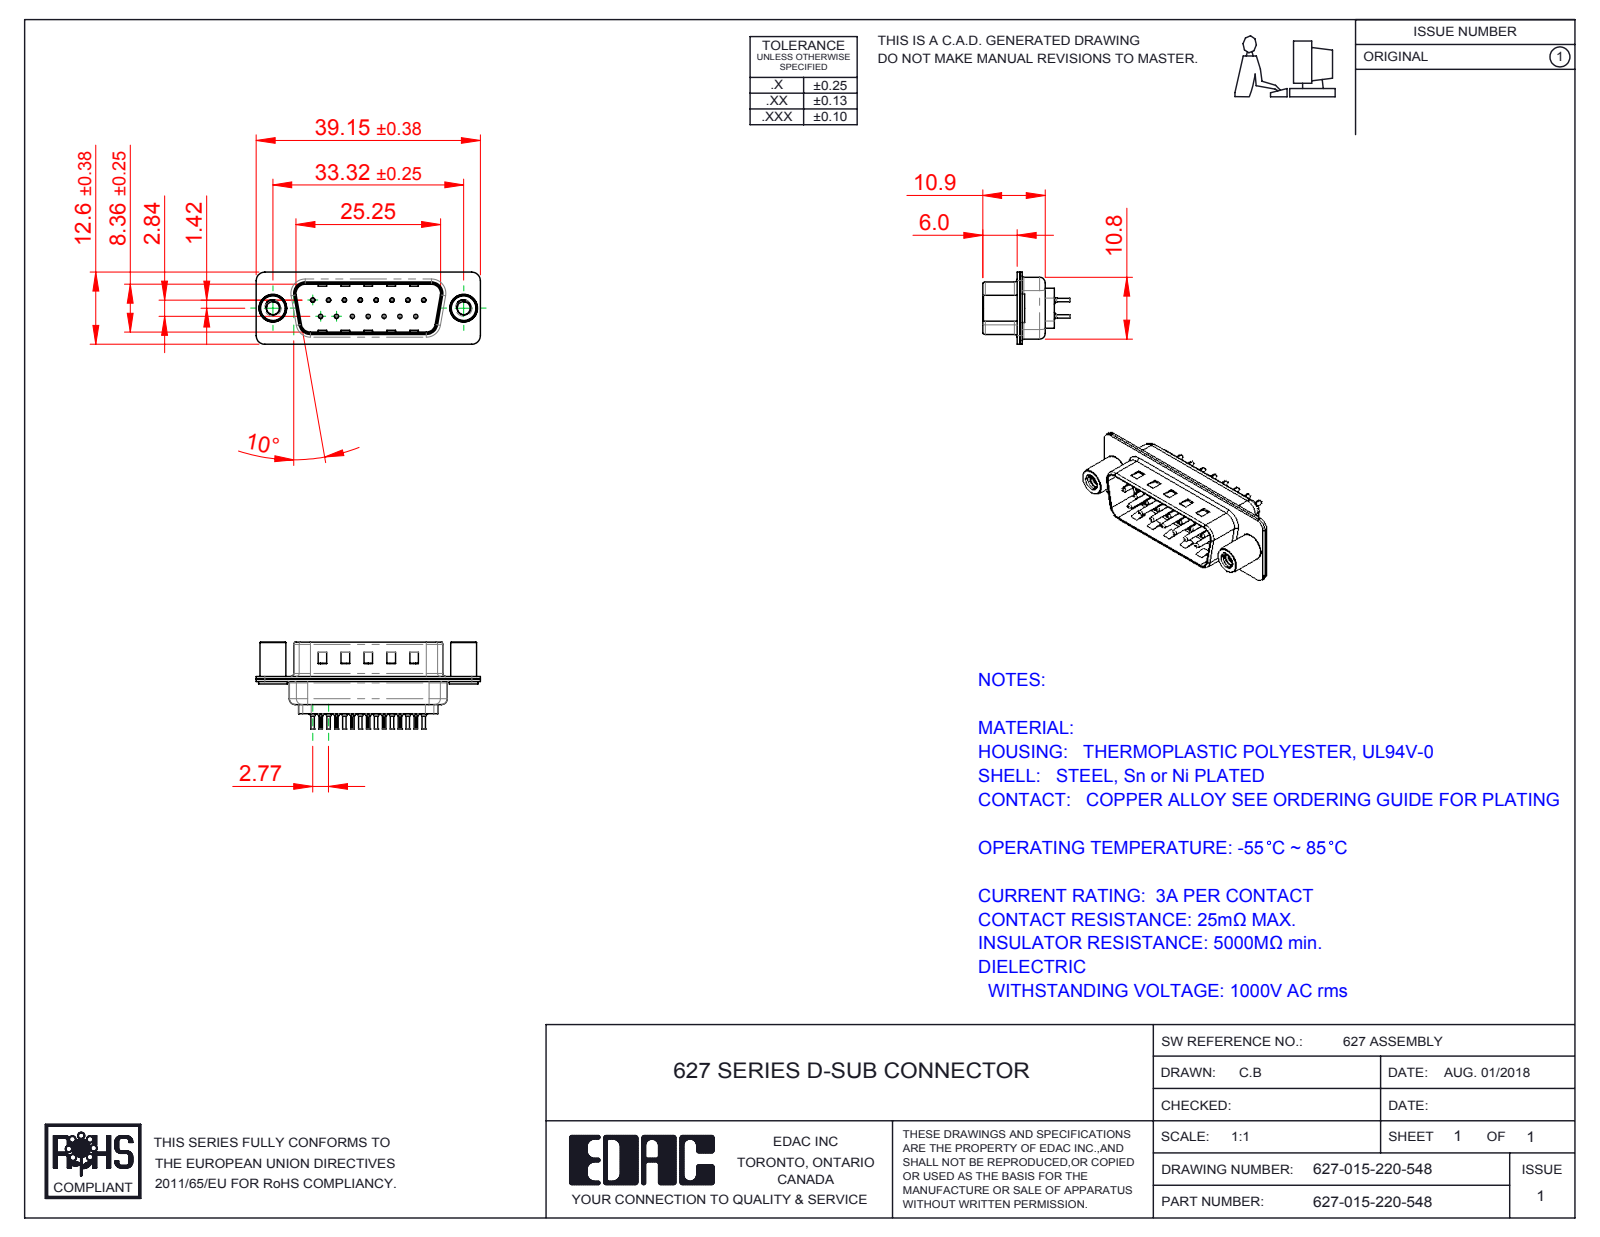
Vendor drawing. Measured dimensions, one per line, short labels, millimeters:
name: 627 Housing_15 LP; 627 Shell Front_15 Contacts; 627 Contact Row 2_20L; 627-015-220-548 (+3 more)
written by: SolidWorks 2016 (CONFIG_CONTROL_DESIGN)
unit: mm
bodies: 20 solids, 1844 faces (501 planar, 716 cylindrical, 627 other)
size: 39.15 × 15.2 × 12.6
volume: 1 887 mm³; area: 5 501 mm²
holes: 15× ⌀0.2, 15× ⌀0.35, 15× ⌀1.1, 15× ⌀1.6, 2× ⌀2.26, 2× ⌀4, 2× ⌀4.8
bosses: 15× ⌀2, 15× ⌀1.5, 15× ⌀0.75, 15× ⌀0.6, 2× ⌀5, 2× ⌀4.9, 2× ⌀4.5
rounds: 30× R0.1, 16× R1.5, 12× R2, 8× R0.5, 8× R1.6, 4× R0.25, 4× R0.6, 4× R0.65
face distances: 0.4, 0.45, 0.9, 0.82, 9.58, 8.76, 1.5, 1.4, 6.5, 5.6
hole spacings: 3.16, 2.77, 5.54, 8.31, 11.08, 5.03, 5.04, 7.48
